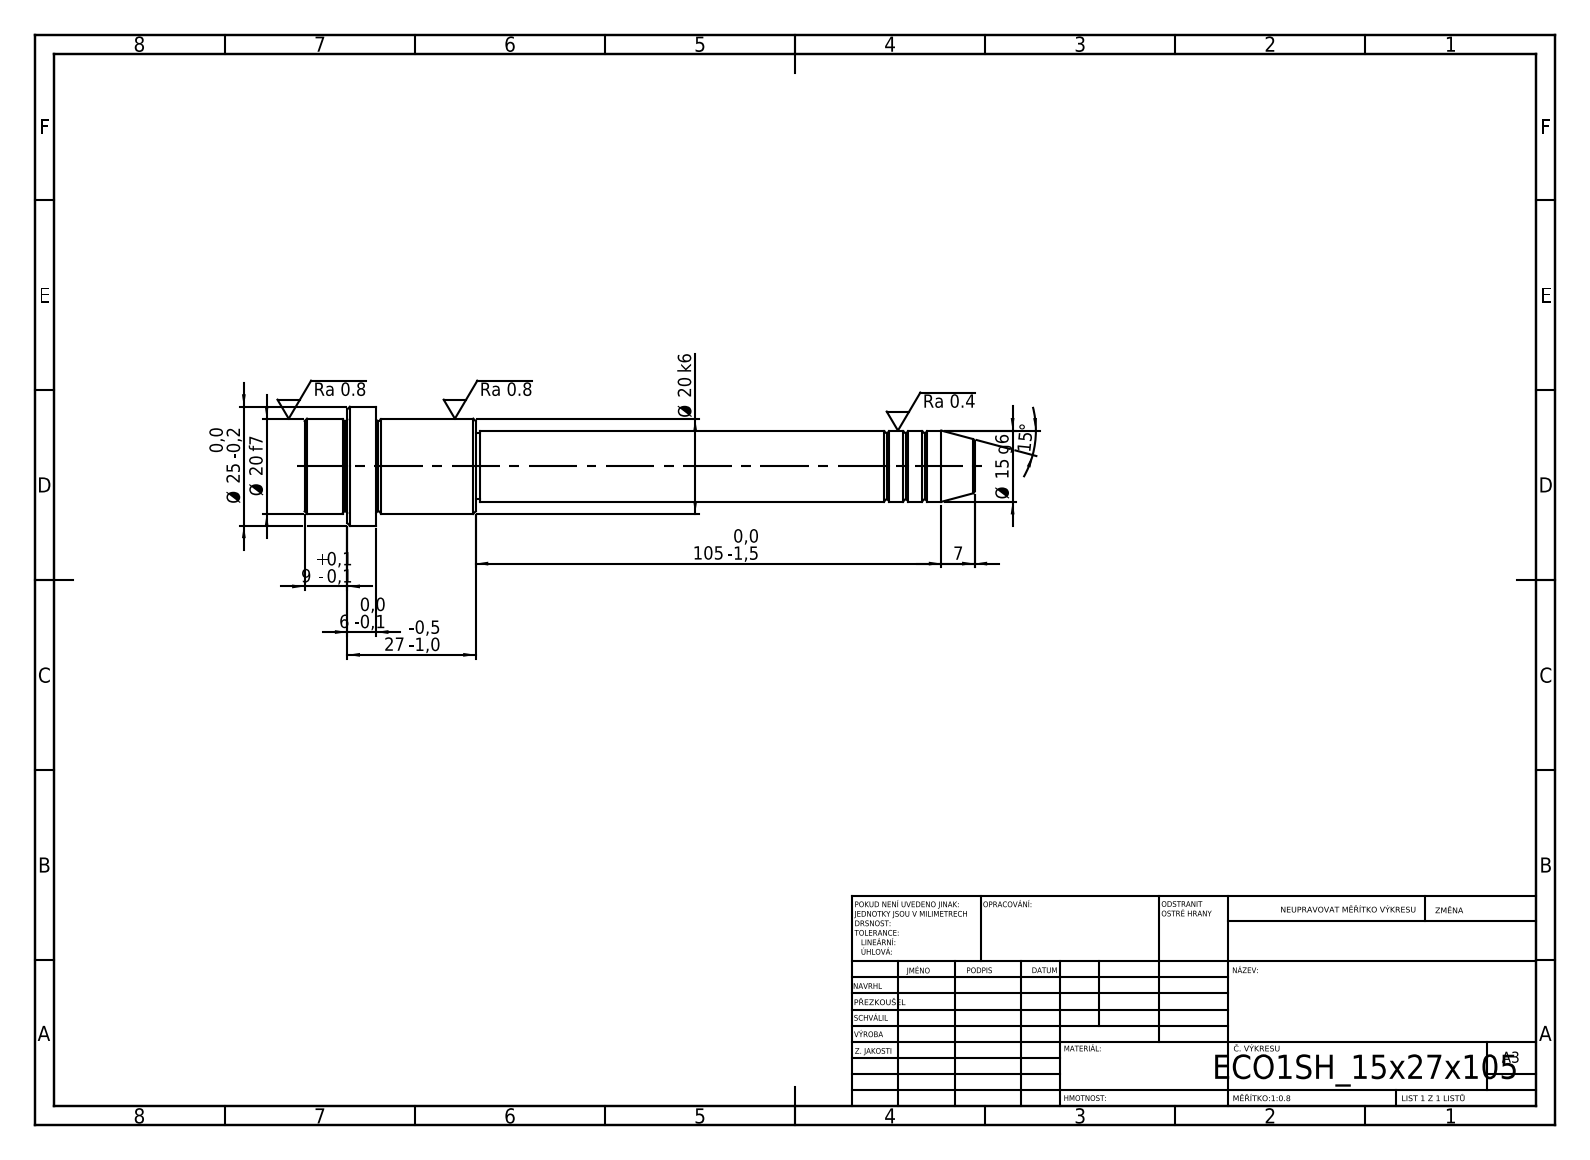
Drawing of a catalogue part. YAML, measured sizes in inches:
step_written_by: "SolidWorks 2019 (CONFIG_CONTROL_DESIGN)"
units: inches
bodies: {solids: 1, faces: 52, planar: 6, cylindrical: 16, other: 30}
overall_size: [5.551, 0.984, 0.984]
volume: 1.861
surface_area: 12.85
round_bosses_or_shafts:
  - {diameter: 0.984, count: 1}
  - {diameter: 0.787, count: 1}
  - {diameter: 0.591, count: 1}
  - {diameter: 0.551, count: 1}
face_to_face_distances: [0.591, 0.236, 0.354, 0.827, 1.063, 1.417, 4.134, 4.961, 5.197, 5.551]
